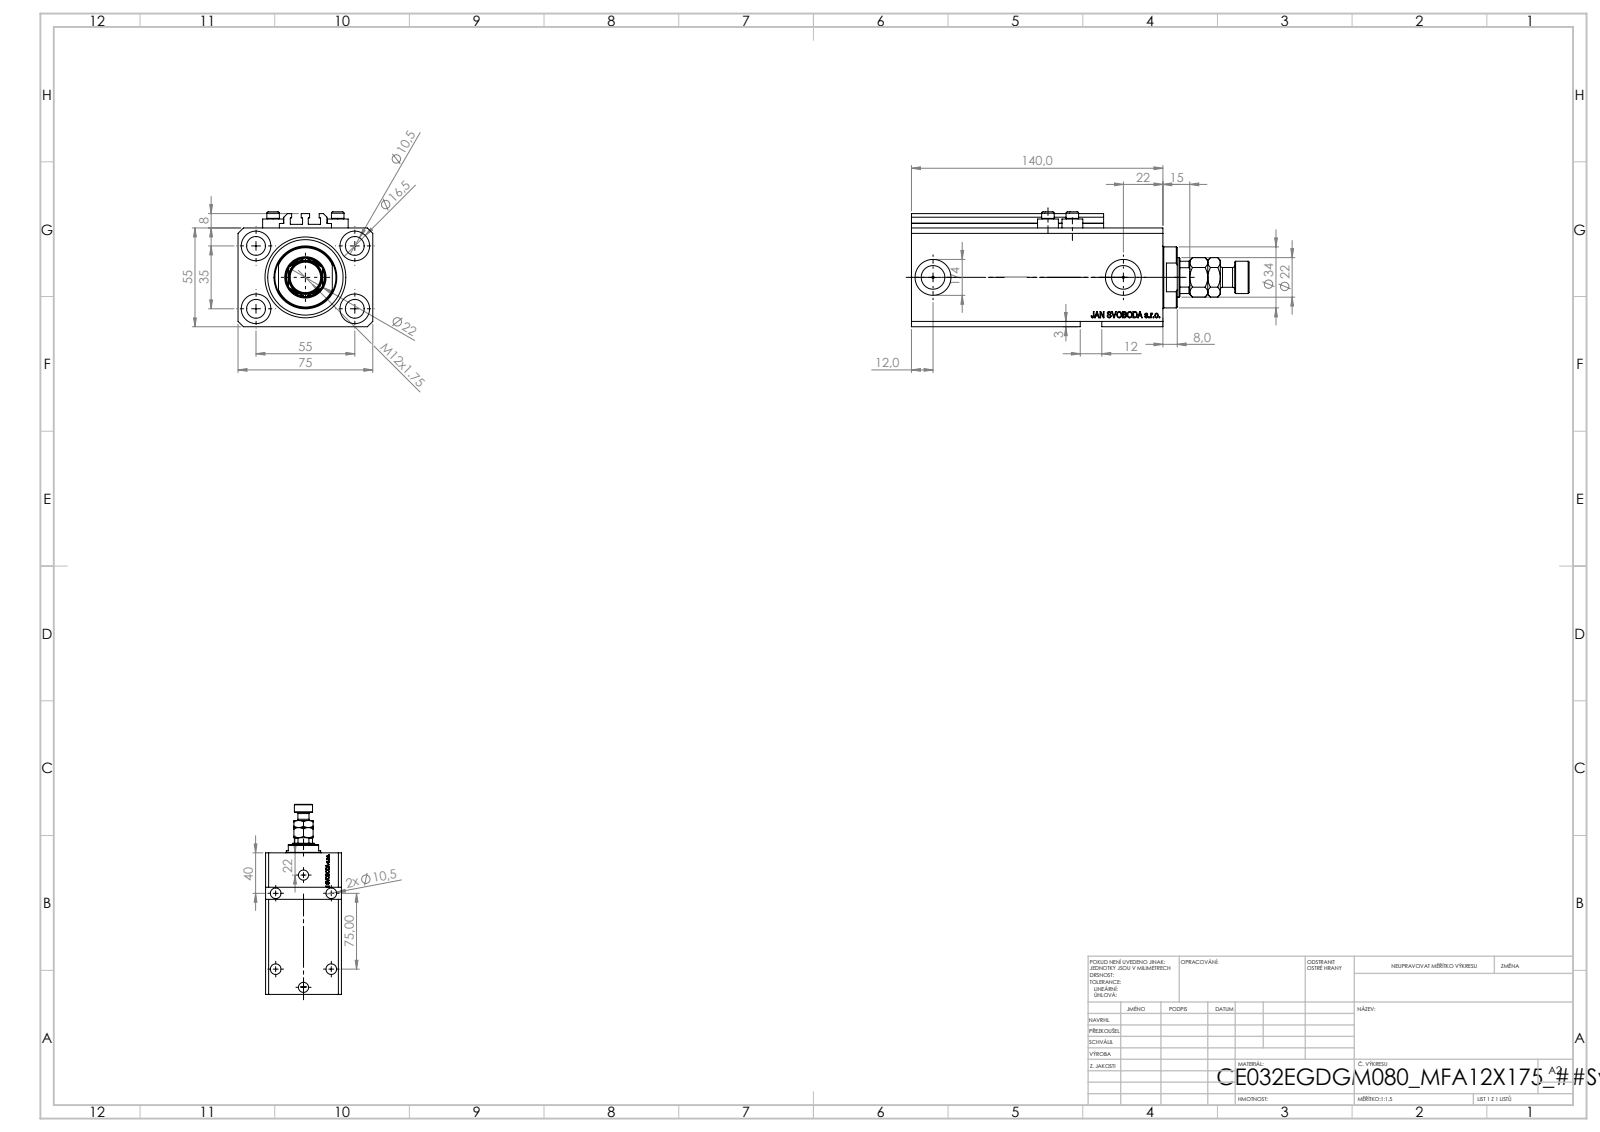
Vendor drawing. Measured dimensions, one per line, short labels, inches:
name: V250CE_VC_E; V250CE_E_Body; MFA; V250CE_C_VCP (+1 more)
written by: SolidWorks 2019 (CONFIG_CONTROL_DESIGN)
unit: in
bodies: 9 solids, 1152 faces (534 planar, 162 cylindrical, 456 other)
size: 7.402 × 2.953 × 2.52
volume: 29.88 in³; area: 184.7 in²
holes: 9× ⌀0.413, 4× ⌀0.049, 4× ⌀0.157, 4× ⌀0.65, 2× ⌀0.394, 2× ⌀0.518, 2× ⌀0.787, 1× ⌀0.866, 1× ⌀1.26, 1× ⌀1.772
bosses: 4× ⌀0.457, 4× ⌀0.276, 1× ⌀1.339, 1× ⌀0.709, 1× ⌀0.433
rounds: 10× R0.008, 1× R0.413
face distances: 2.165, 2.953, 0.591, 0.39, 5.512, 4.921, 0.098, 2.244, 0.118, 0.315
hole spacings: 1.283, 1.294, 2.165, 3.818, 0.535, 0.555, 1.016, 1.283
